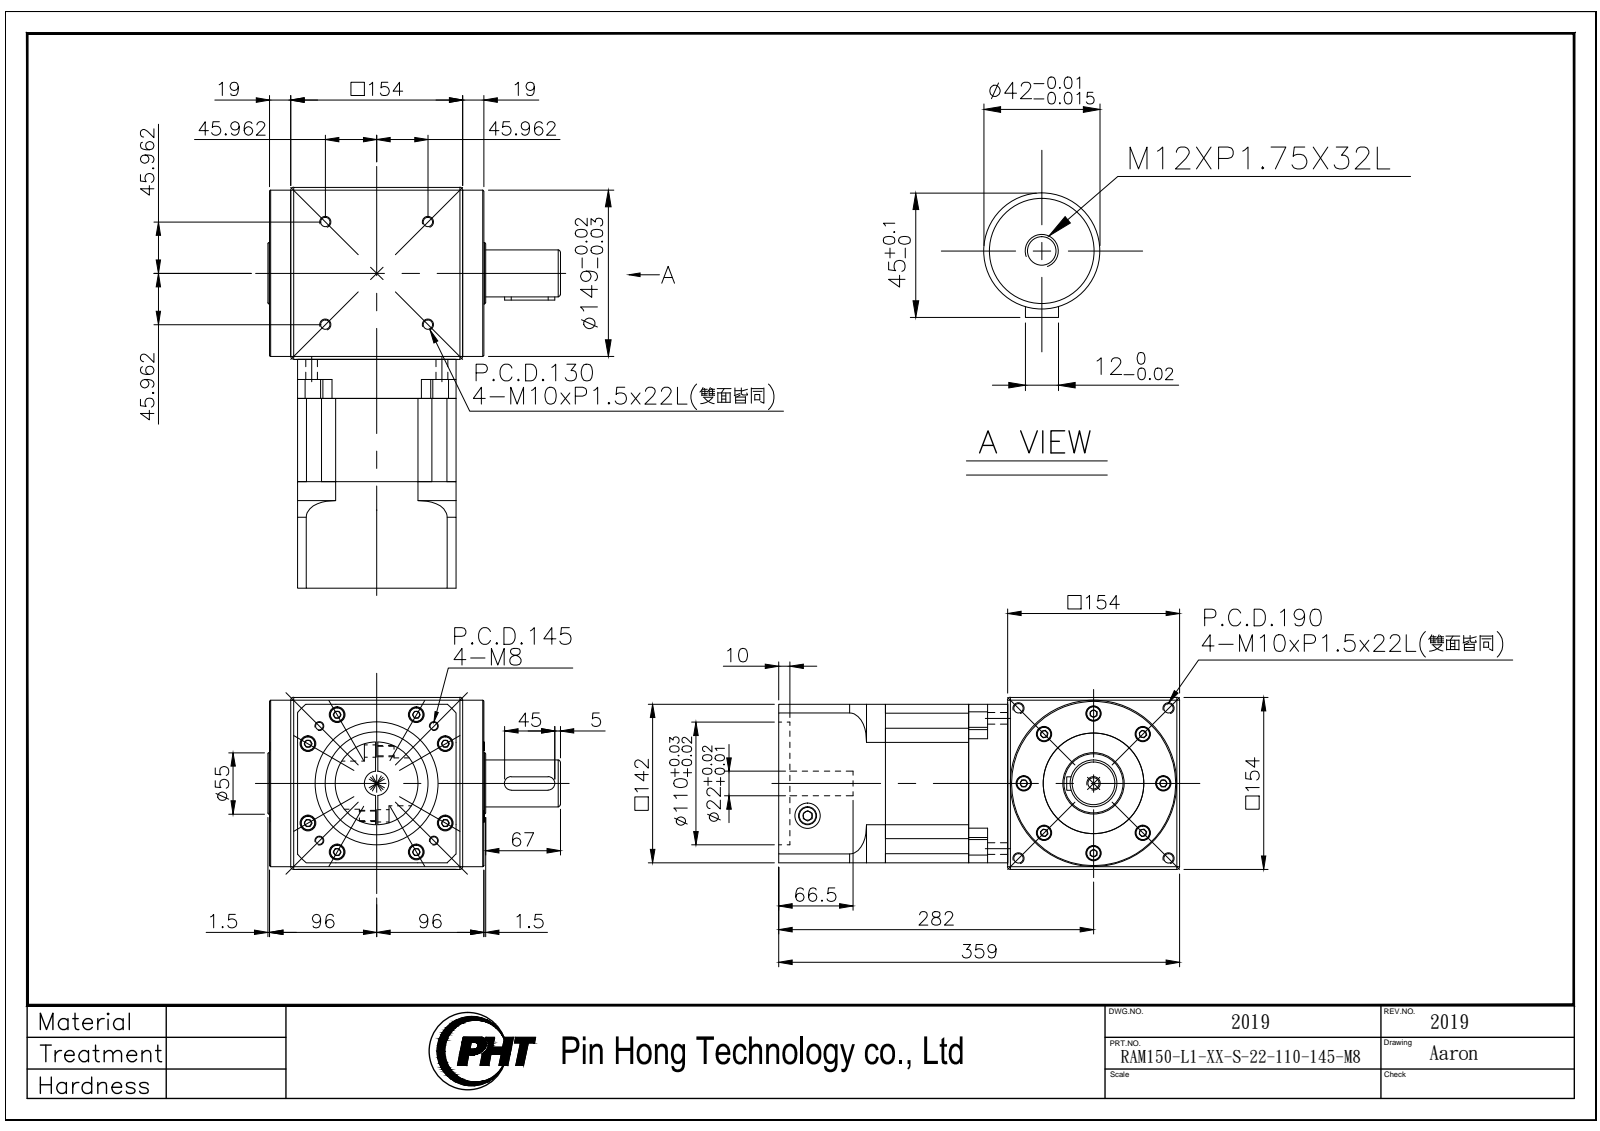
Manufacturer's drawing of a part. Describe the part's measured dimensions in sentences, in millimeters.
The part is named "RAM150-L1-XX-S-22-110-145-M8_2019". Its 3-D file was written by "SolidWorks 2016 (AUTOMOTIVE_DESIGN)". It is 5 solids with 882 faces: 429 planar, 293 cylindrical and 160 other. Overall it measures 359 by 262 by 154 millimeters. Its volume is 7 918 000 cubic millimeters and its surface area 517 520 square millimeters. Round holes: 12 of diameter 8.5, 8 of diameter 9, 8 of diameter 11, 8 of diameter 14, 8 of diameter 17.5, 4 of diameter 6.8, 4 of diameter 10.5, 2 of diameter 22.5, 1 of diameter 4.08, 1 of diameter 10.2, 1 of diameter 22, 1 of diameter 92. Round bosses or shafts: 12 of diameter 16, 8 of diameter 13, 1 of diameter 149, 1 of diameter 130, 1 of diameter 90, 1 of diameter 74, 1 of diameter 55, 1 of diameter 42. Partial cylindrical surfaces (rounded edges, fillets, slot ends): 4 of radius 10, 2 of radius 6, 1 of radius 80, 1 of radius 95, 1 of radius 107.4. The main face-to-face distances are 6, 148, 154, 142, 74.5, 35, 109.5, 263.5, 189, 167. The hole center spacings are 71, 18.72, 18.79, 23.06, 47.83, 67.34, 82.93, 87.37.
